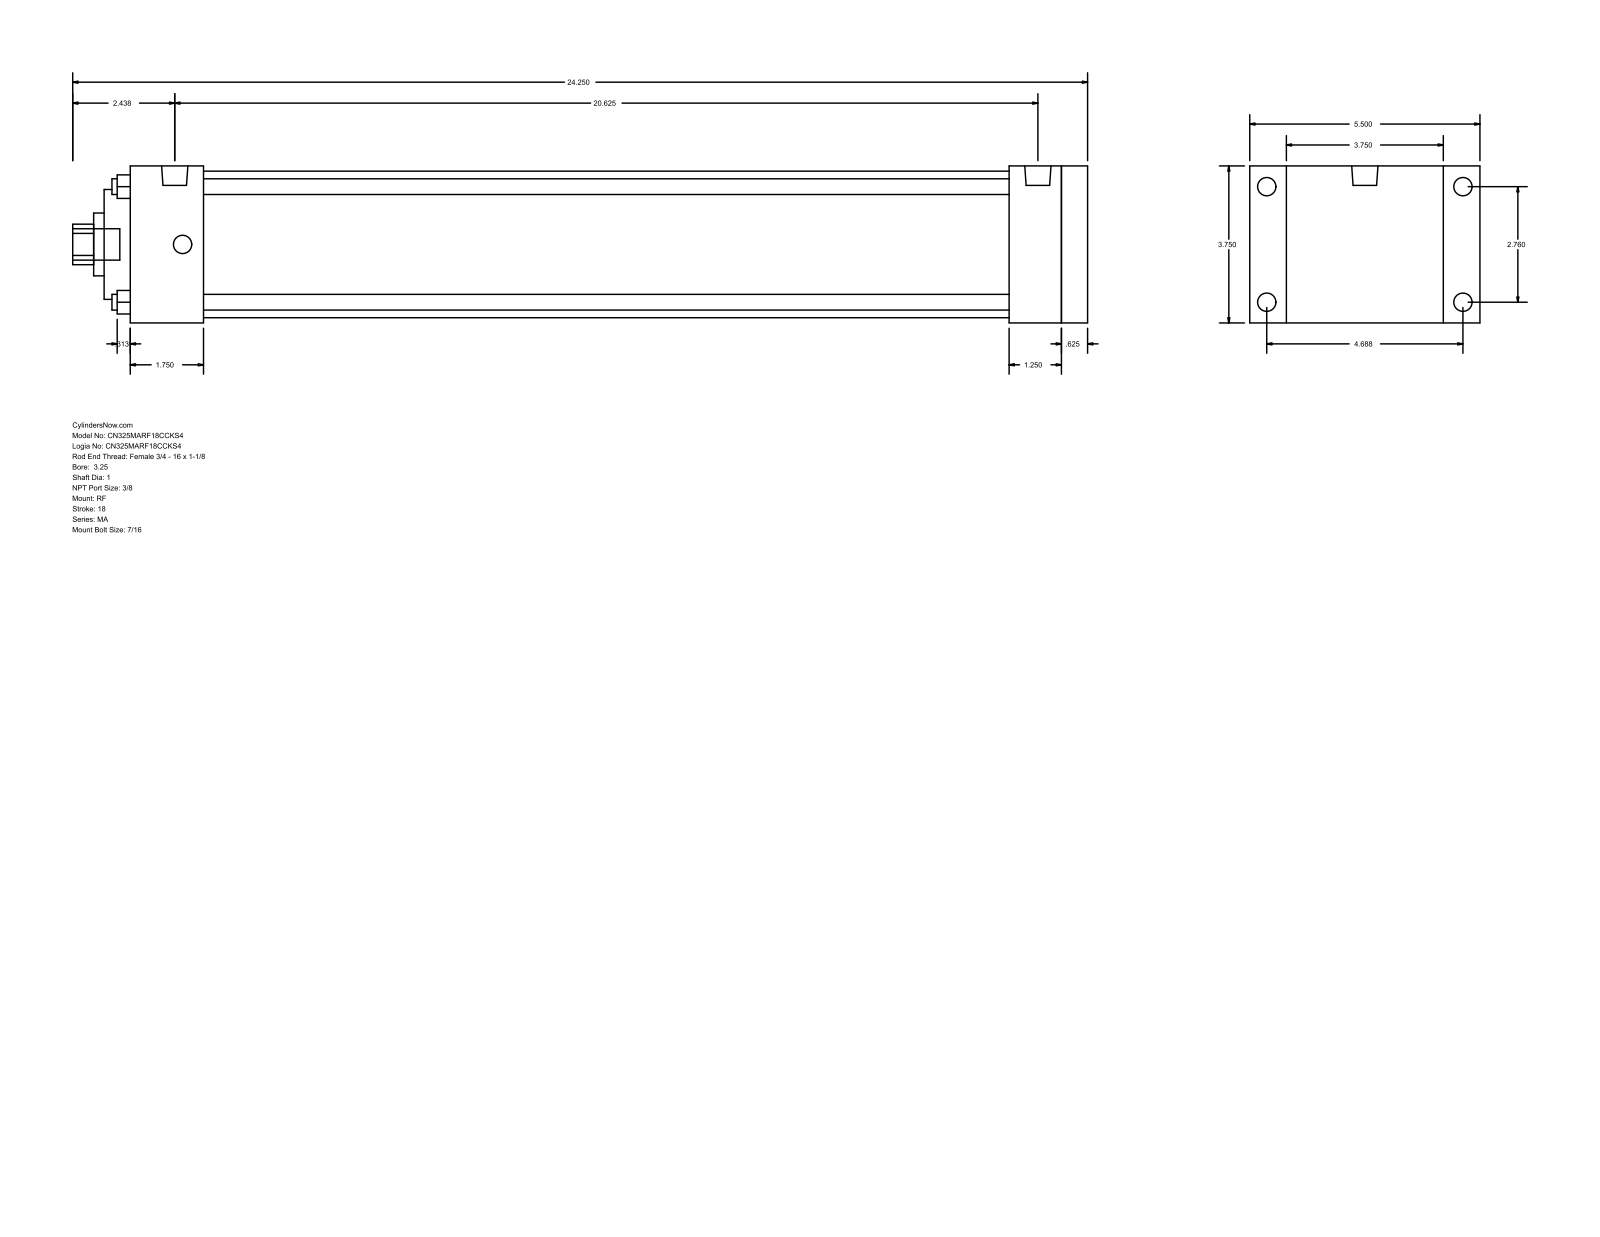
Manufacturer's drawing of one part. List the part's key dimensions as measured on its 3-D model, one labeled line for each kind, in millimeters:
Part name (STEP PRODUCT): MA_RF__0325_1
STEP written by: GSSL Pune (CONFIG_CONTROL_DESIGN)
Units: millimetres
Bodies: 0 solids, 94 faces (65 planar, 29 cylindrical, 0 other)
Overall size (bounding box): 615.95 × 139.7 × 95.25
Round holes (diameter × count): ⌀9.53 ×4, ⌀25.4 ×1, ⌀38.1 ×1, ⌀66.67 ×1, ⌀88.9 ×1
Round bosses / shafts (diameter × count): ⌀11.11 ×8, ⌀15.93 ×2, ⌀19.05 ×1
Partial cylindrical surfaces — rounded edges, fillets, slot ends (radius × count): R12.29 ×1
Main face-to-face distances: 95.24, 581.03, 15.87, 565.16, 22.23, 117.47, 533.41, 31.75, 47.62, 44.46
Hole centre spacings: 49.57, 70.1, 99.14
